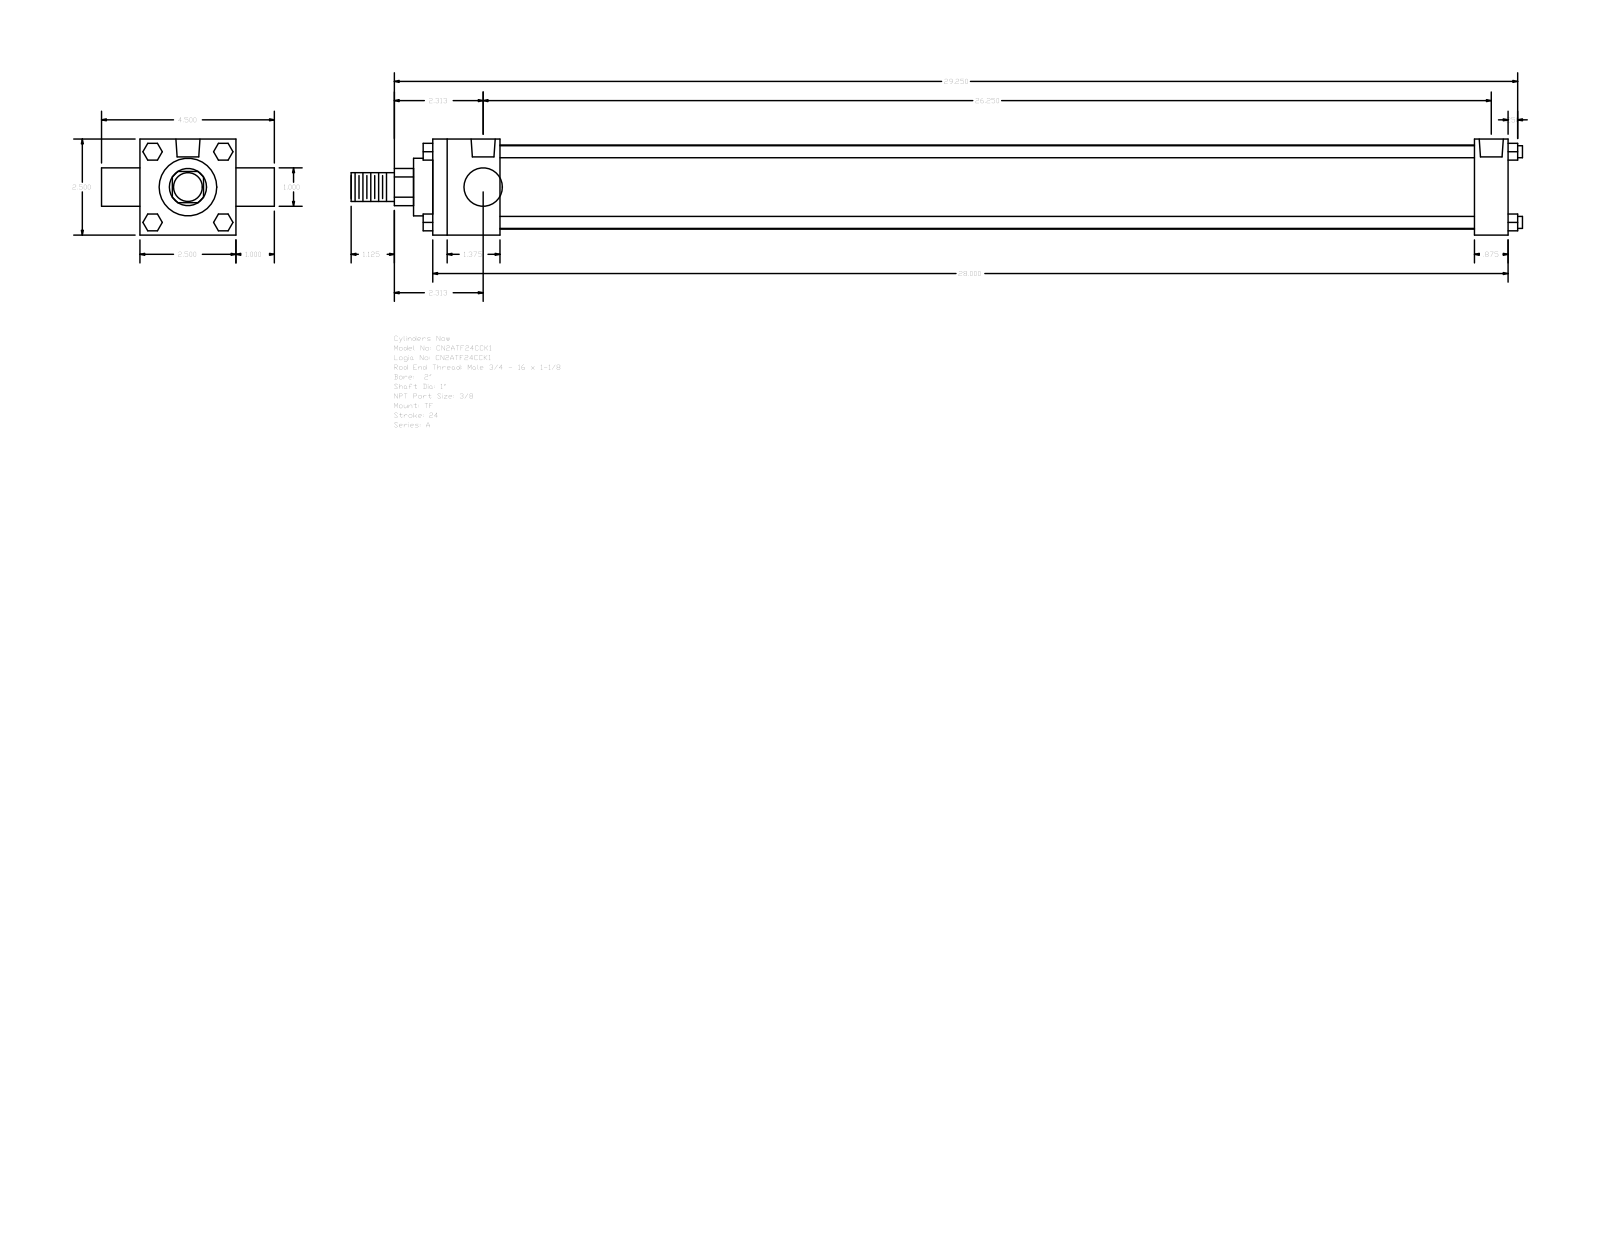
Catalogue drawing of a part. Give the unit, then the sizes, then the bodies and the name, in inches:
Units: inches
Overall size (bounding box): 30.5 × 4.5 × 2.5
Round holes (diameter × count): ⌀0.219 ×3, ⌀0.627 ×2
Round bosses / shafts (diameter × count): ⌀0.313 ×4, ⌀1 ×2, ⌀2.19 ×1, ⌀1.5 ×1, ⌀0.75 ×1
Partial cylindrical surfaces — rounded edges, fillets, slot ends (radius × count): R0.484 ×1
Main face-to-face distances: 2.5, 28, 1.75, 27.125, 25.375, 26.25, 0.875, 1, 3.5, 28.5
Hole centre spacings: 0.063, 0.157, 26.031, 26.093, 26.187, 26.25
Bodies: 0 solids, 120 faces (92 planar, 28 cylindrical, 0 other)
Part name (STEP PRODUCT): A_TF__0200_1
STEP written by: GSSL Pune (CONFIG_CONTROL_DESIGN)
